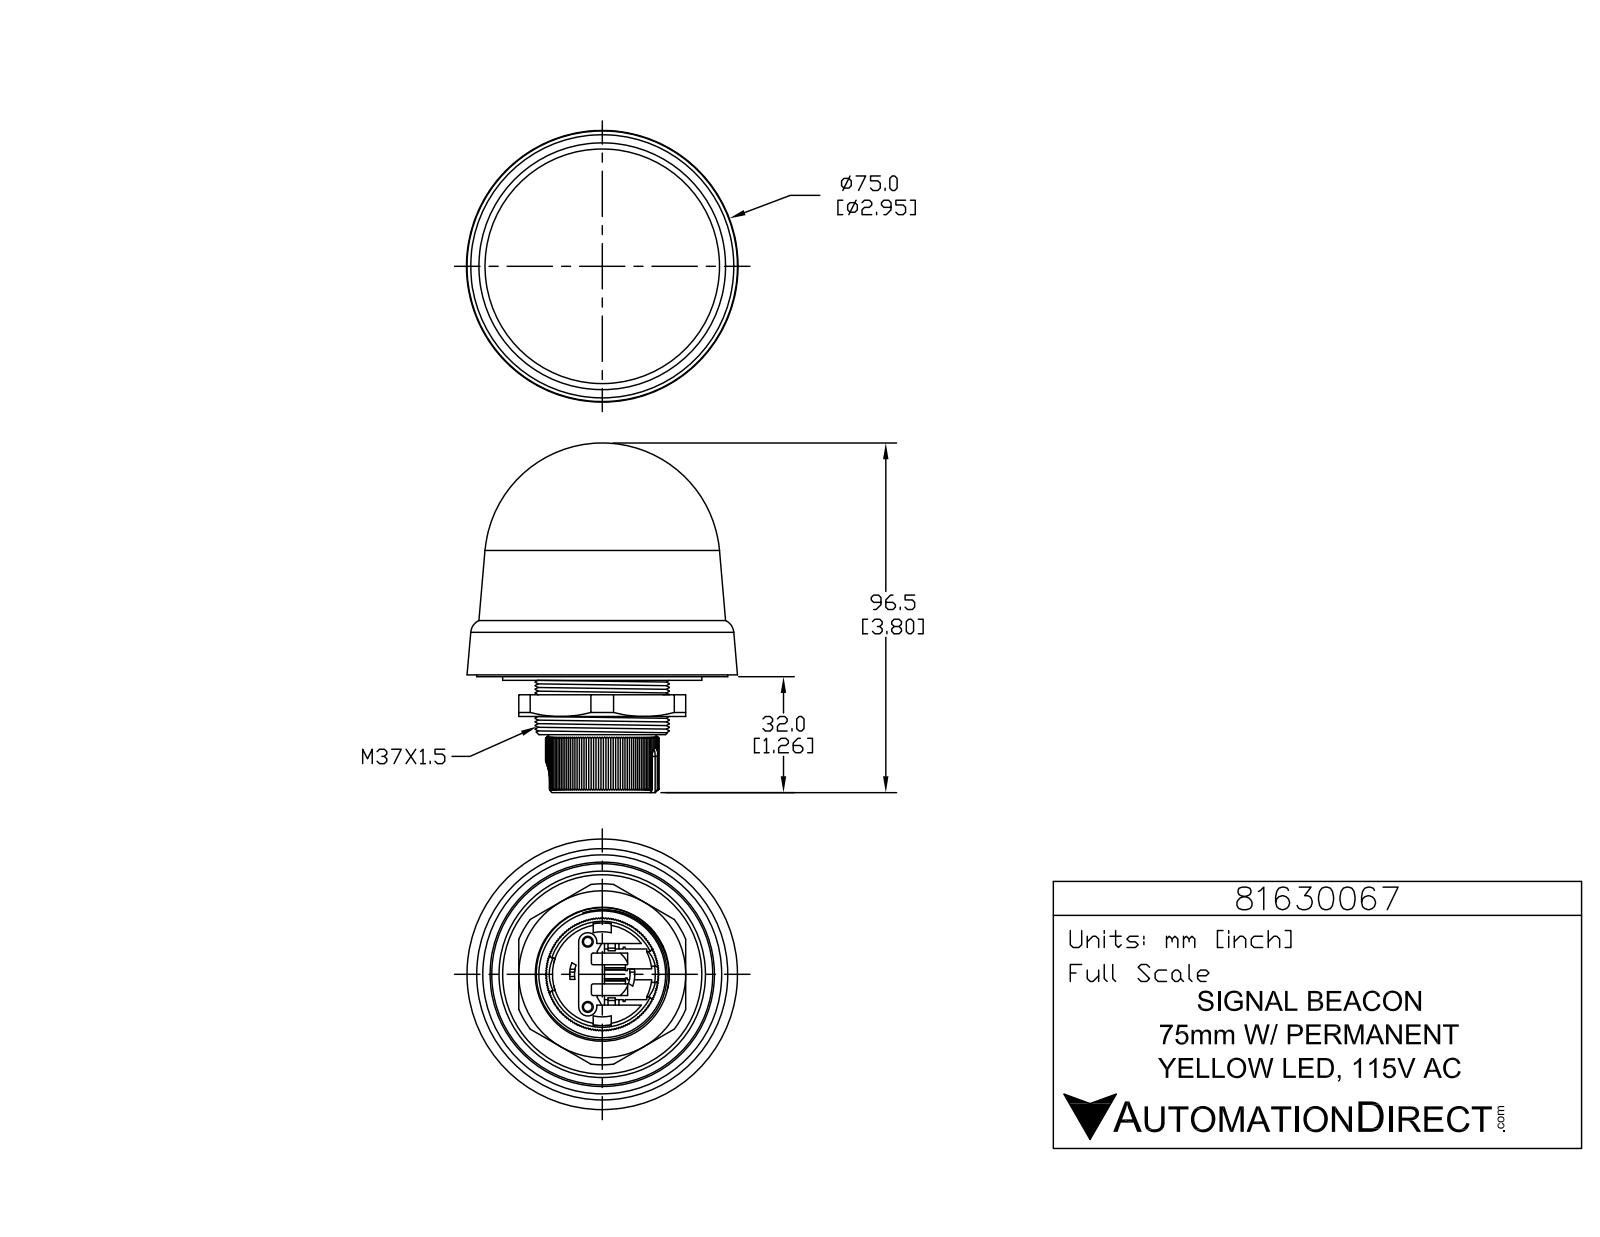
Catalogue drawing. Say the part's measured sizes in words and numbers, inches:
The part is named "81630067". Its 3-D file was written by "SolidWorks 2019 (CONFIG_CONTROL_DESIGN)". It is 3 solids with 560 faces: 432 planar, 80 cylindrical and 48 other. Overall it measures 3.799 by 2.941 by 2.941 inches. Its volume is 12.36 cubic inches and its surface area 58.68 square inches. Round holes: 2 of diameter 0.094, 2 of diameter 0.118, 1 of diameter 0.604, 1 of diameter 1.142. Round bosses or shafts: 2 of diameter 0.217, 2 of diameter 0.067, 1 of diameter 2.165, 1 of diameter 1.457, 1 of diameter 0.925. Partial cylindrical surfaces (rounded edges, fillets, slot ends): 6 of radius 0.008, 6 of radius 0.039, 4 of radius 0.02, 2 of radius 0.031, 2 of radius 0.079, 2 of radius 0.098, 1 of radius 0.177, 1 of radius 0.354. The main face-to-face distances are 0.177, 0.354, 0.197, 0.433, 0.512, 0.335, 0.059, 0.394, 0.118, 0.157. The hole center spacings are 0.388, 0.709.
